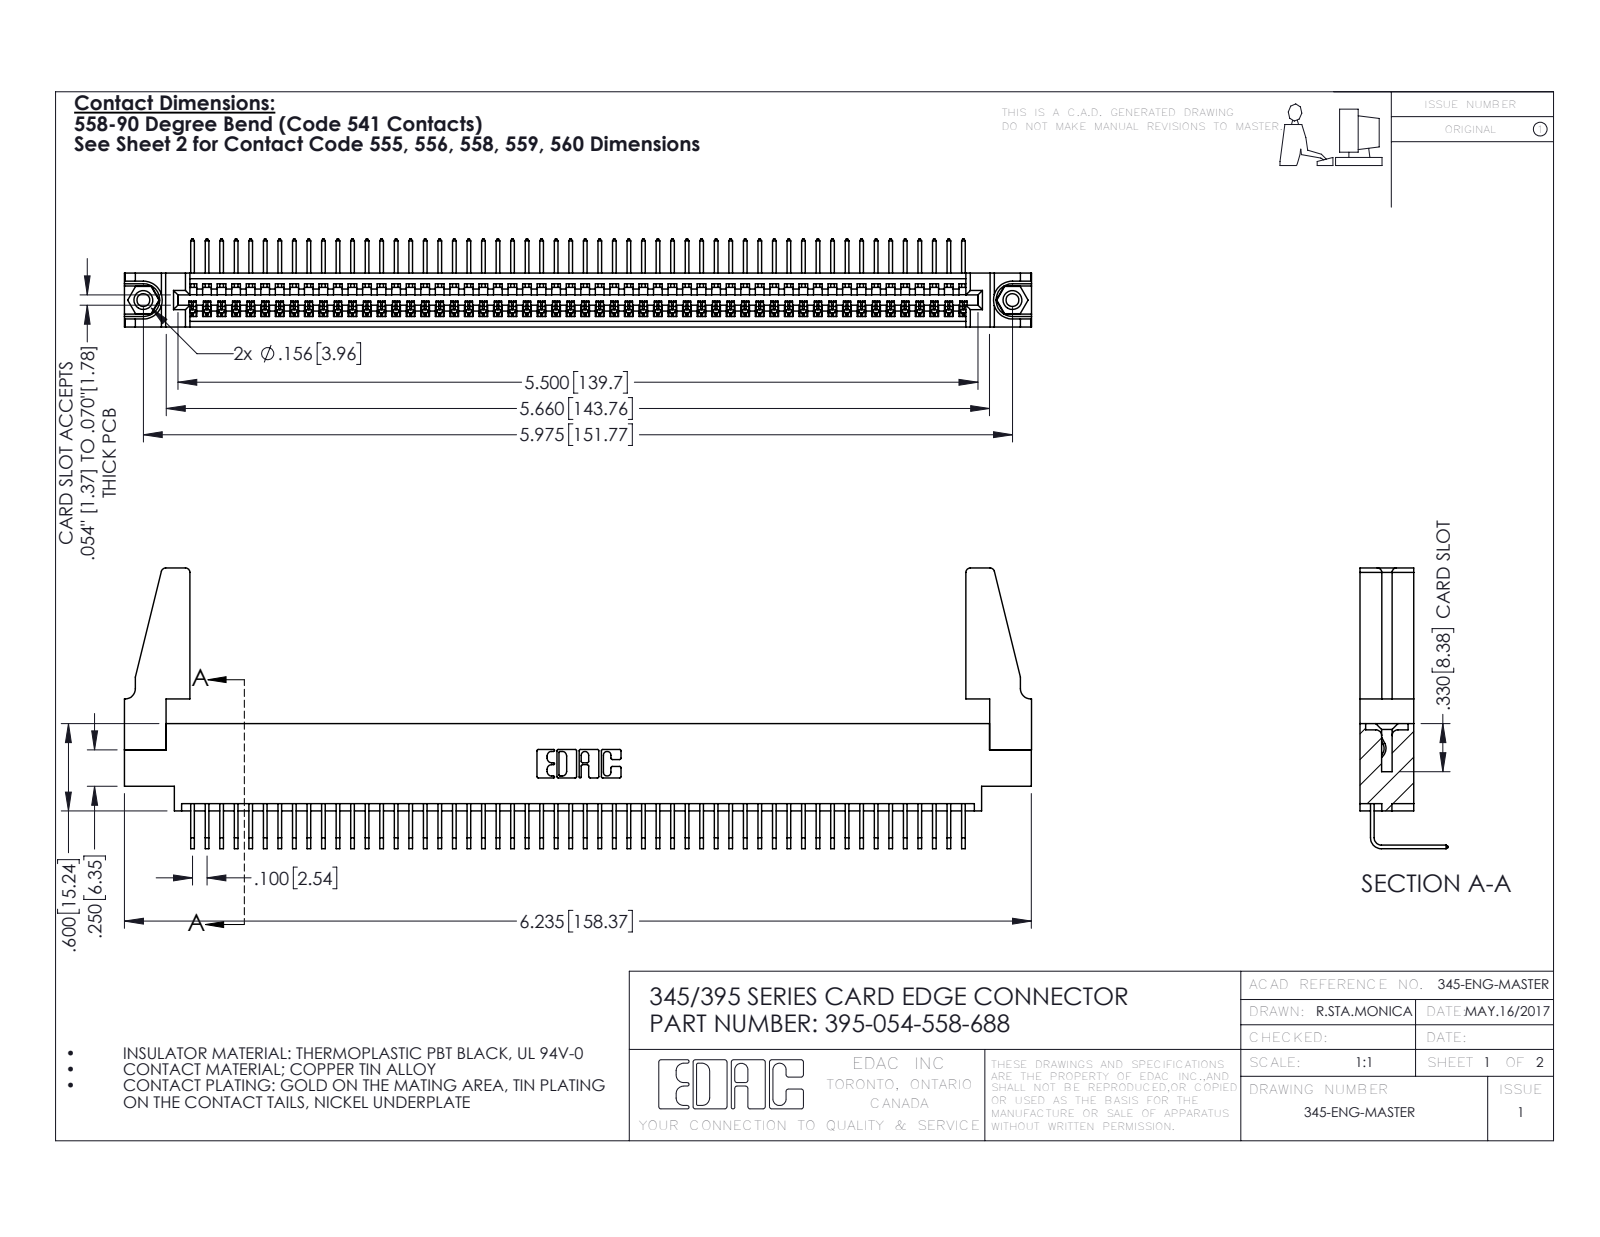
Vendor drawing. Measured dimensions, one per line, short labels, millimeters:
name: 345-220-078_345-220-088; 345-292-001_558 Tail - 2; 395-054-558-688; 345-250-001_345-250-001-102 (+1 more)
written by: SolidWorks 2016 (CONFIG_CONTROL_DESIGN)
unit: mm
bodies: 59 solids, 3494 faces (2424 planar, 1054 cylindrical, 16 other)
size: 158.4 × 49 × 15.4
volume: 18 470 mm³; area: 24 690 mm²
holes: 2× ⌀2.3, 2× ⌀3.2, 2× ⌀4, 1× ⌀1.6
bosses: 2× ⌀3.9
rounds: 108× R0.2, 22× R0.3, 8× R0.8, 6× R0.2, 6× R0.8, 3× R0.7, 2× R0.8, 2× R1
face distances: 1.8, 7.6, 9.4, 5.1, 2.5, 6.9, 0.6, 5.7, 4.4, 3.8
hole spacings: 6.9, 145.8, 151.8
